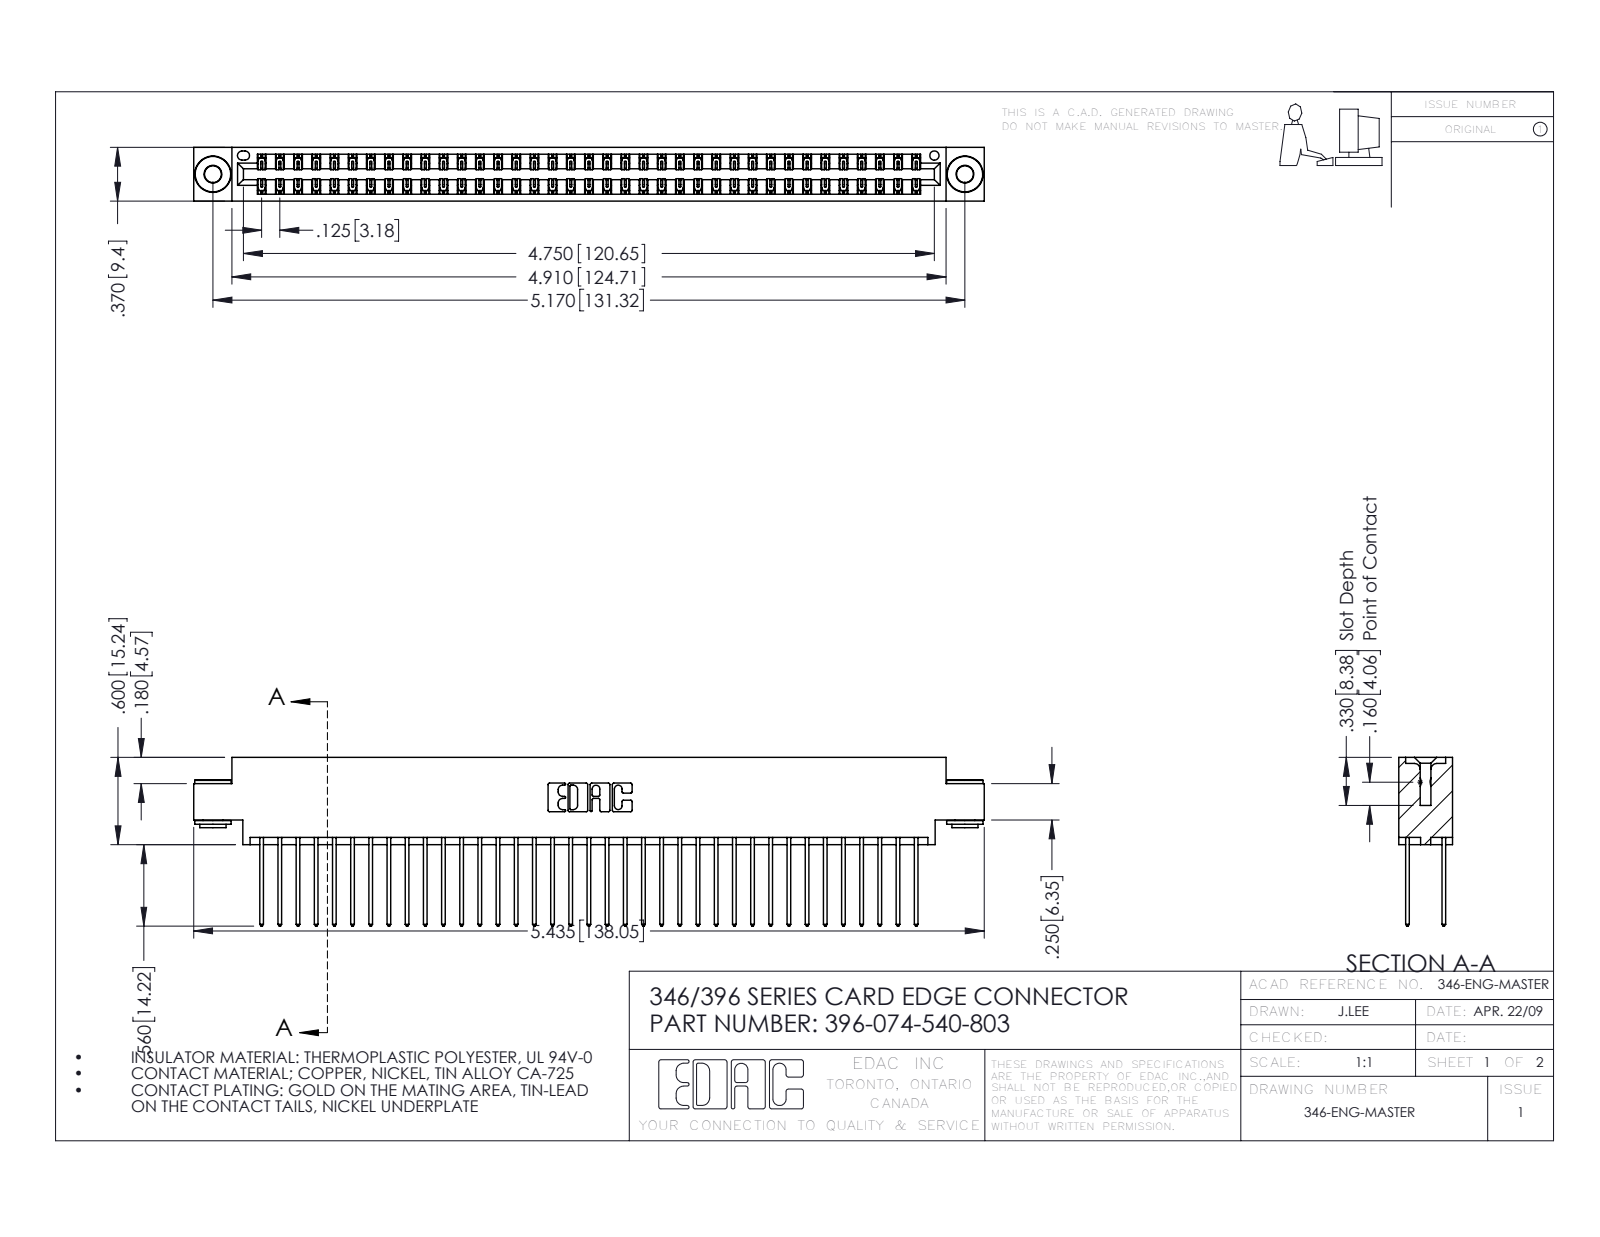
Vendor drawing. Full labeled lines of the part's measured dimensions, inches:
Part name (STEP PRODUCT): 396-074-540-803; 346 Part_0.170 Offset - 0.156 Dia-TH; 345-250-002_345-250-002-102; 345-292-001_345-293-140
STEP written by: SolidWorks 2016 (CONFIG_CONTROL_DESIGN)
Units: inches
Bodies: 77 solids, 4012 faces (2680 planar, 1324 cylindrical, 8 other)
Overall size (bounding box): 5.435 × 1.16 × 0.37
Volume: 0.828 in³ · Surface area: 31.45 in²
Round holes (diameter × count): ⌀0.116 ×2, ⌀0.156 ×2, ⌀0.064 ×1
Round bosses / shafts (diameter × count): ⌀0.25 ×2, ⌀0.18 ×2, ⌀0.136 ×2
Partial cylindrical surfaces — rounded edges, fillets, slot ends (radius × count): R0.006 ×111, R0.01 ×74, R0.01 ×22, R0.007 ×6, R0.031 ×6, R0.026 ×3, R0.014 ×2, R0.022 ×2
Main face-to-face distances: 0.048, 0.322, 0.25, 0.025, 0.37, 0.072, 0.298, 0.275, 0.148, 0.222
Hole centre spacings: 0.246, 4.961, 5.17
